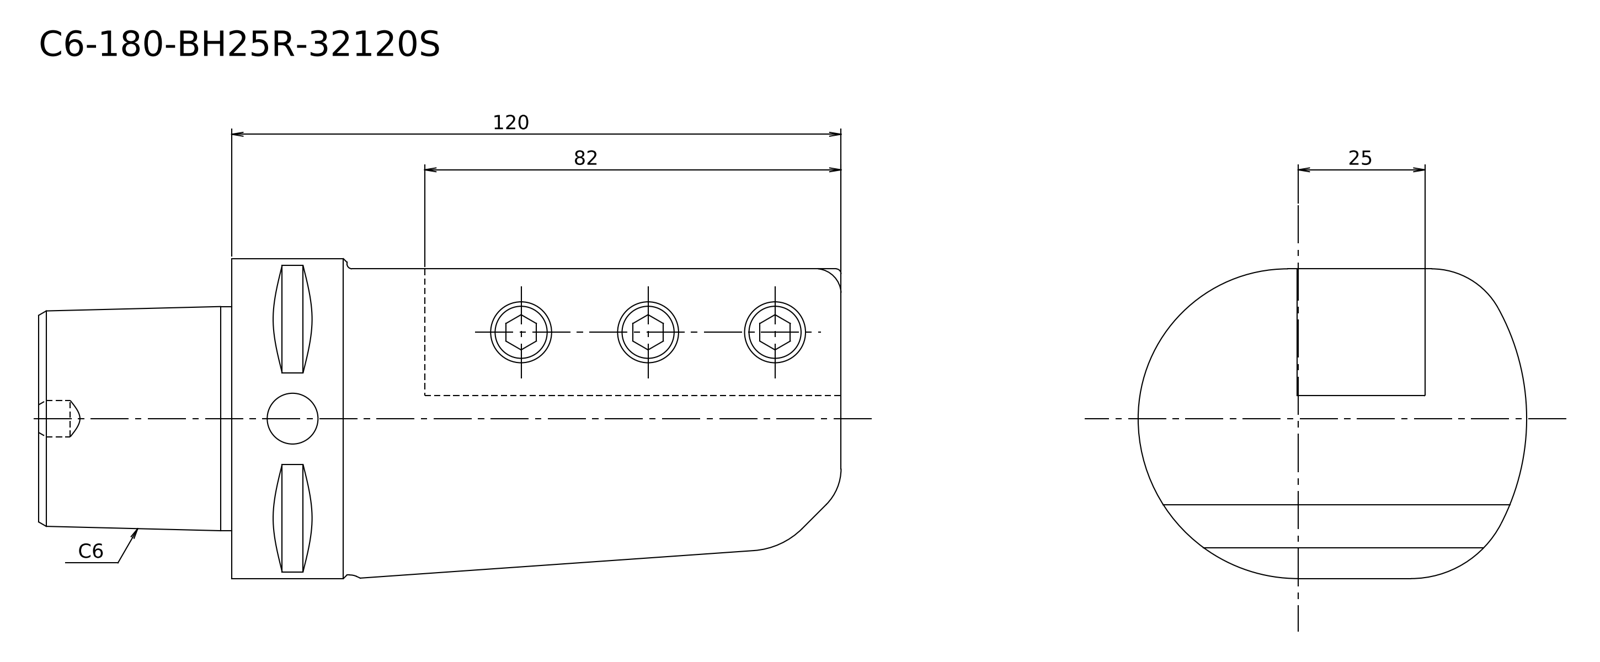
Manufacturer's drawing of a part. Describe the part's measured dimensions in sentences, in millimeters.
The part is named "240[2]". Its 3-D file was written by "Kubotek KeyCreator 2011 V10.0.2 (22737) (automotive_design)". It is 1 solid with 24 faces: 12 planar, 6 cylindrical and 6 other. Overall it measures 158 by 76.5 by 62.98 millimeters. Its volume is 438 068 cubic millimeters and its surface area 42 414 square millimeters. Round bosses or shafts: 1 of diameter 62.98. Partial cylindrical surfaces (rounded edges, fillets, slot ends): 1 of radius 15, 1 of radius 20, 1 of radius 29.5, 1 of radius 31.5, 1 of radius 45. The main face-to-face distances are 25, 38, 120, 158, 82, 76, 87, 5, 33, 71.
